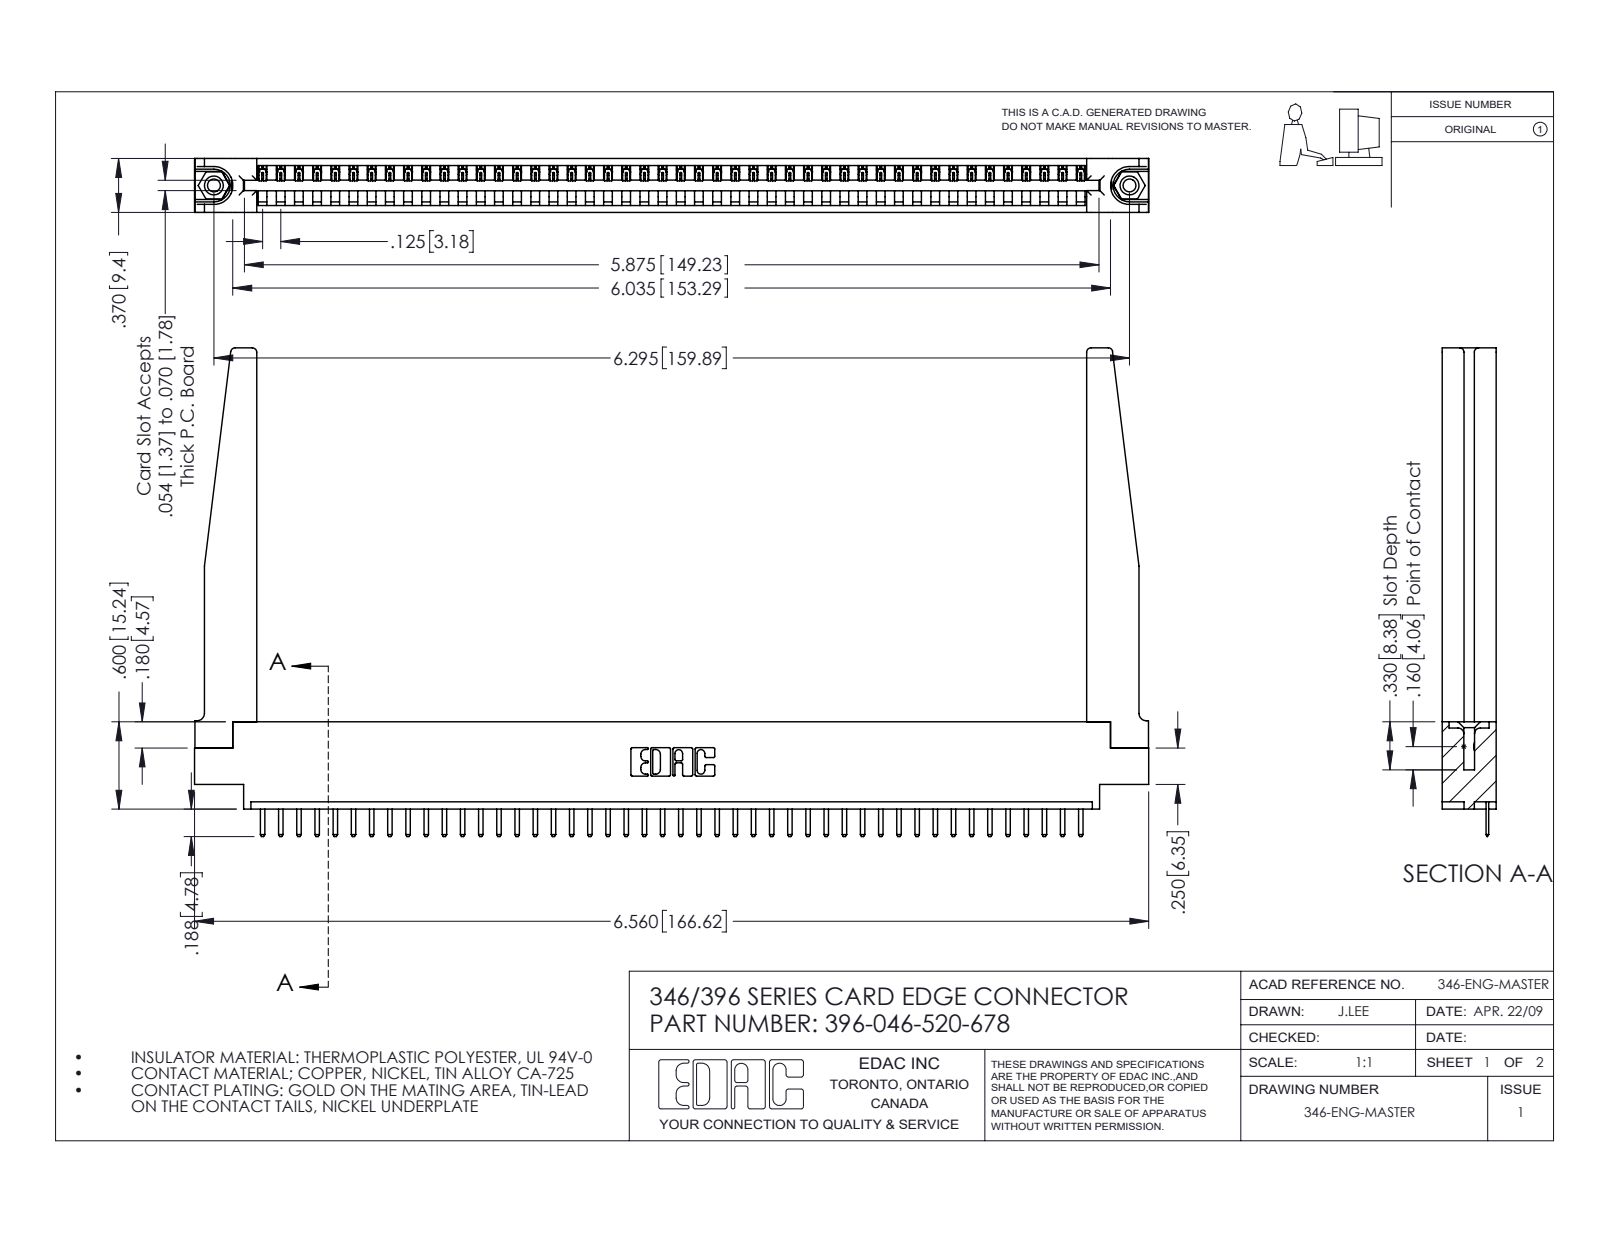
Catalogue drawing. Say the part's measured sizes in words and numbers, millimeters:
The part is named "346-220-078_345-220-078; 345-292-001_345-293-120; 346 Part_0.170 Offset - 0.156 Dia-TH; 396-046-520-678 (+1 more)". Its 3-D file was written by "SolidWorks 2016 (CONFIG_CONTROL_DESIGN)". It is 51 solids with 3212 faces: 2154 planar, 1006 cylindrical and 52 other. Overall it measures 166.6 by 85.3 by 9.4 millimeters. Its volume is 22 600 cubic millimeters and its surface area 25 910 square millimeters. Round holes: 2 of diameter 2.3, 2 of diameter 3.2, 2 of diameter 4, 1 of diameter 1.6. Round bosses or shafts: 2 of diameter 3.9. Partial cylindrical surfaces (rounded edges, fillets, slot ends): 94 of radius 0.3, 92 of radius 0.2, 22 of radius 0.3, 8 of radius 0.8, 6 of radius 0.2, 6 of radius 0.8, 3 of radius 0.7, 2 of radius 0.8. The main face-to-face distances are 9.4, 1.2, 8.2, 3.8, 1.8, 3.8, 6.4, 5.6, 2.5, 4.4. The hole center spacings are 6.2, 154.6, 159.9.
